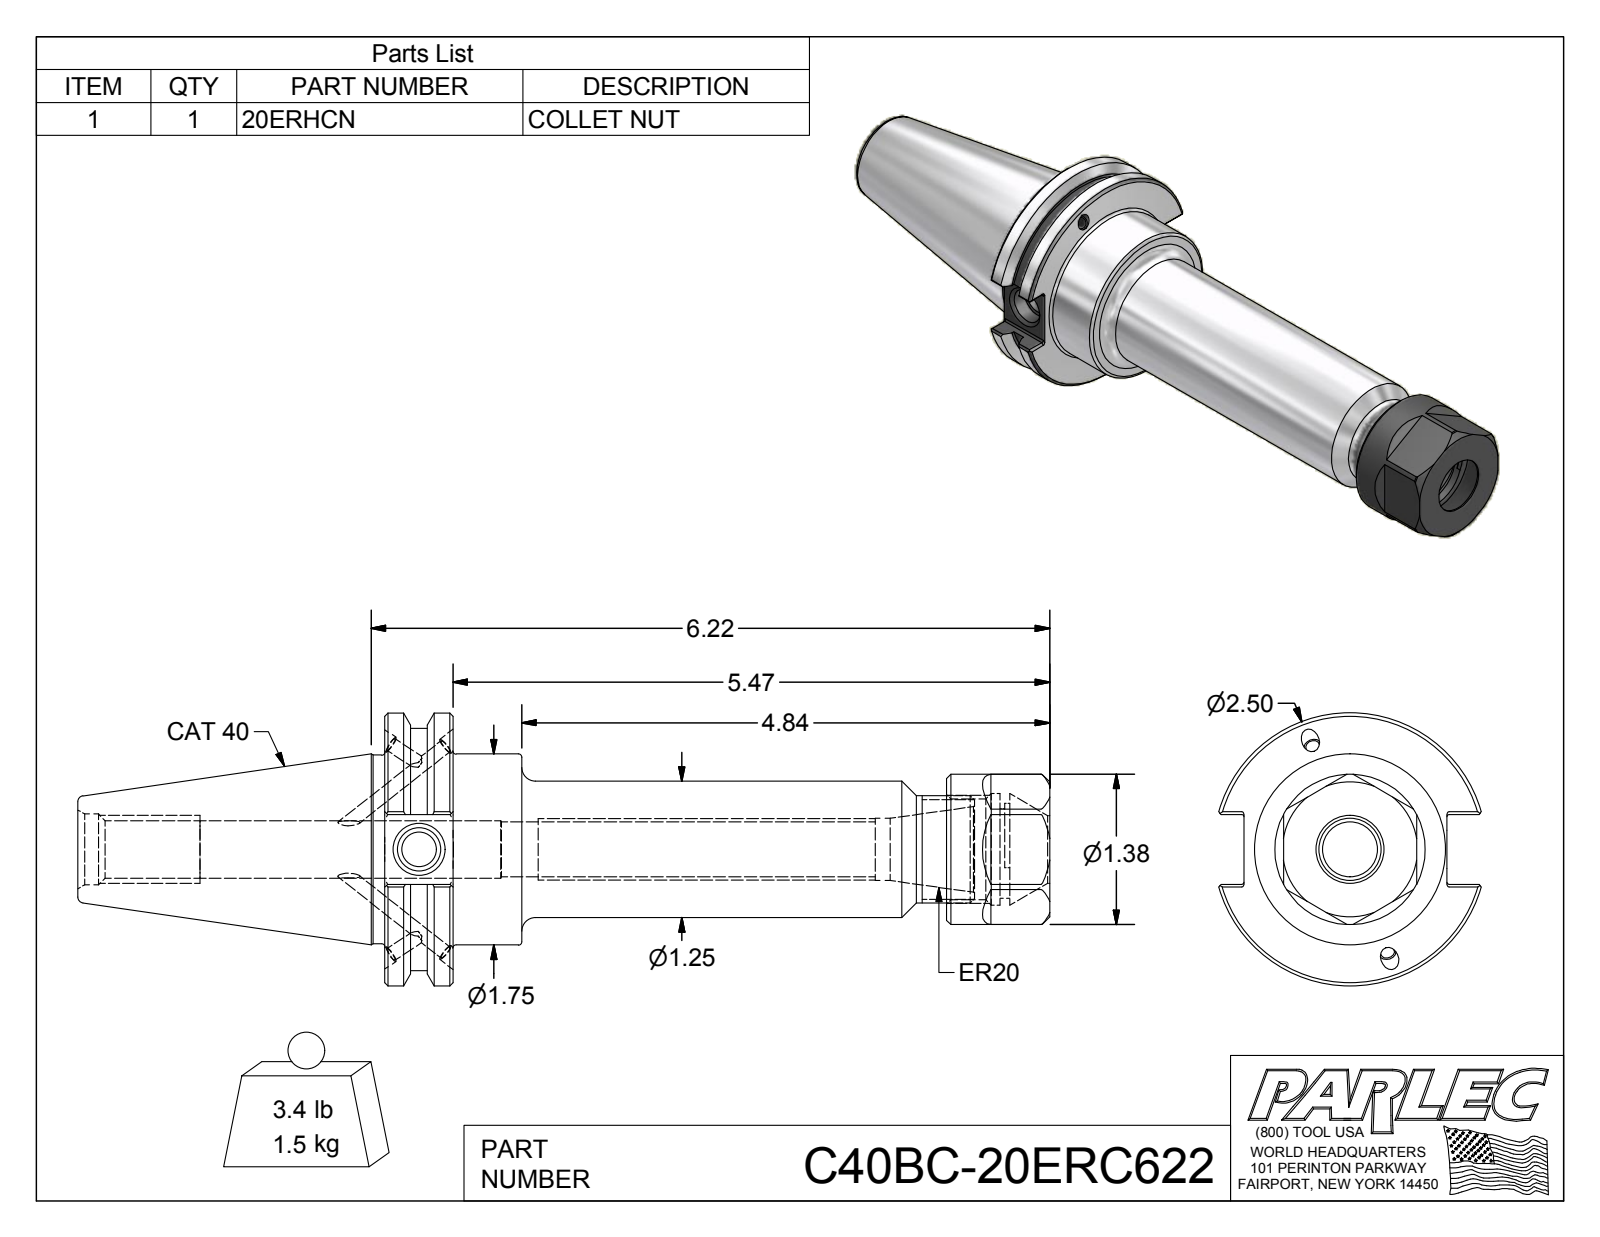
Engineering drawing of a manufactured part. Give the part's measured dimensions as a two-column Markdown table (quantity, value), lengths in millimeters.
| quantity | value |
| --- | --- |
| part name | C40BCB-20ER6-1; 029-965; 20ERHCN; C40BC-20ERC622 |
| STEP written by | Autodesk Inventor 2016 (AUTOMOTIVE_DESIGN) |
| units | millimeters |
| bodies | 6 solids, 201 faces (94 planar, 55 cylindrical, 52 other) |
| overall size | 226.25 × 63.5 × 61.05 |
| volume | 196 146 mm³ |
| surface area | 43 963 mm² |
| round holes (diameter × count) | 3.3 × 4, 4.1 × 4, 8 × 1, 10.13 × 1, 12.75 × 1, 13.36 × 1, 13.39 × 1, 14.48 × 1, 15.76 × 1, 16.46 × 1, 20.83 × 1, 23.5 × 1 |
| round bosses / shafts (diameter × count) | 4.2 × 4, 4 × 4, 63.5 × 1, 56.36 × 1, 44.45 × 1, 43.94 × 1, 35 × 1, 31.75 × 1 |
| partial cylindrical surfaces (radius × count) | 0.51 × 12, 10.75 × 1 |
| main face-to-face distances | 15.87, 31, 130.81, 114.94, 31.88, 16.01, 98.93, 154.81, 138.94, 122.93 |
| hole center spacings | 0.94 |
